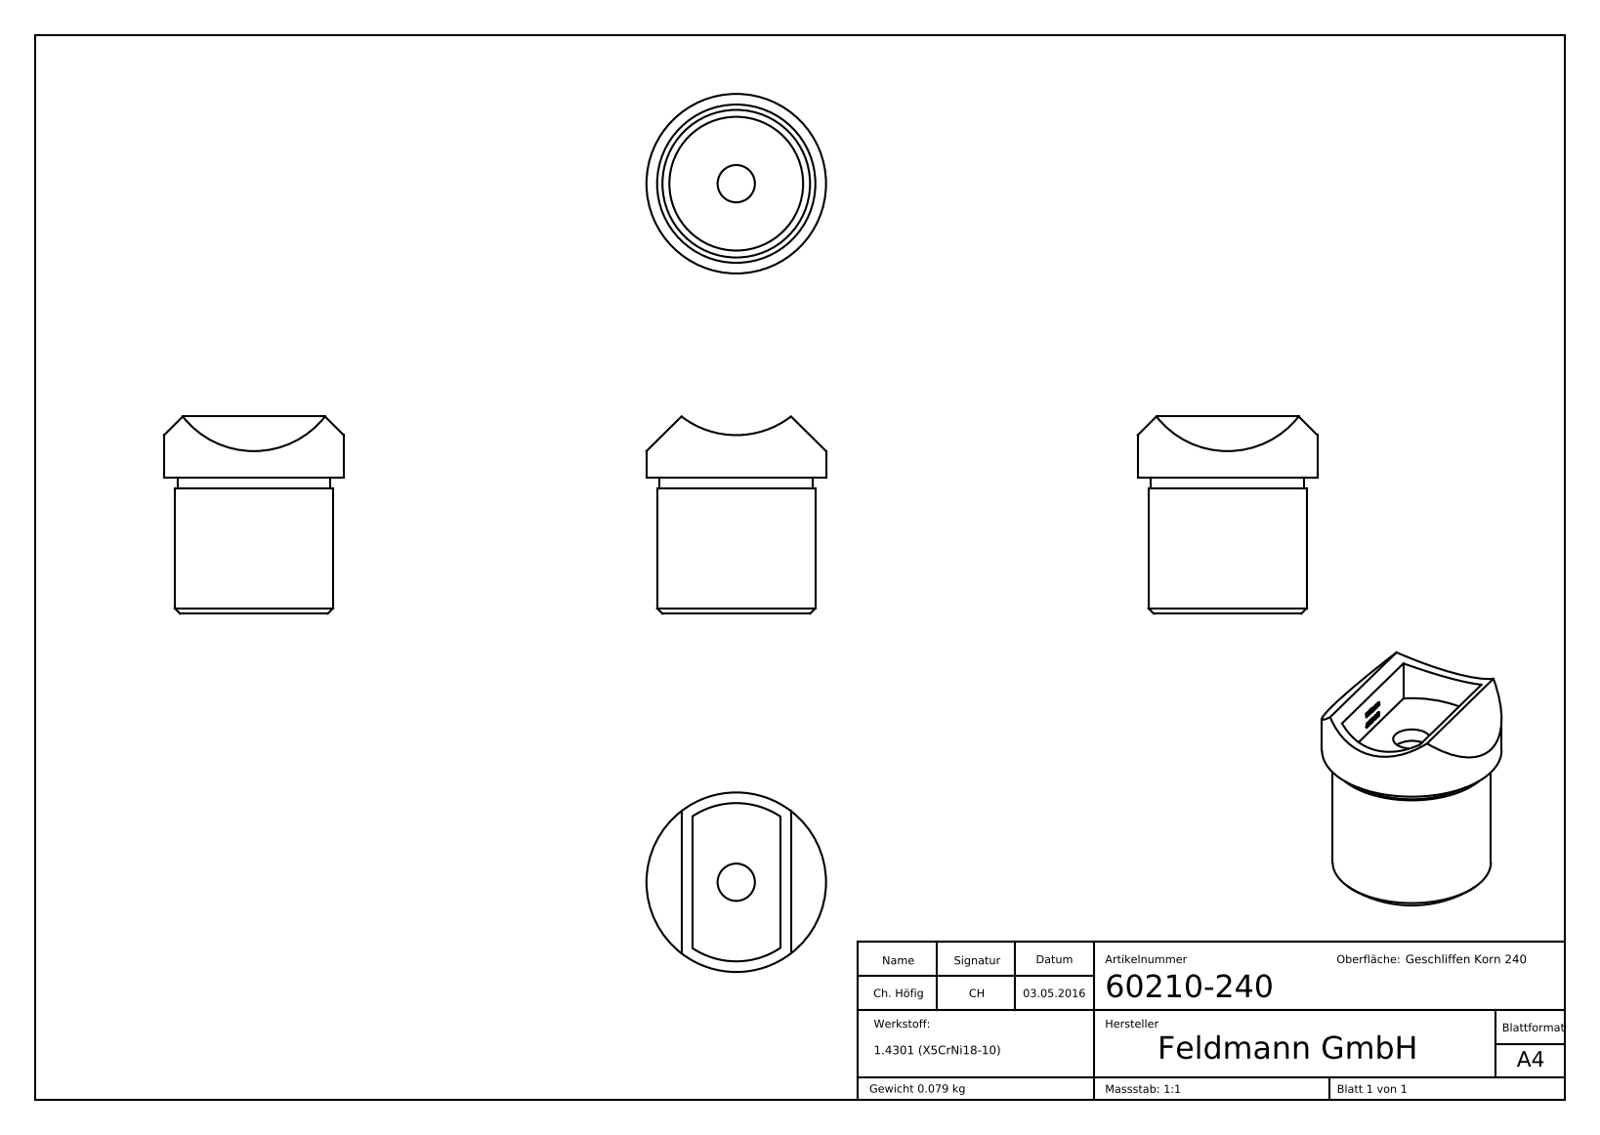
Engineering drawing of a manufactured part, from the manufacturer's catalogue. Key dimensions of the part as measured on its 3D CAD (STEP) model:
Part name (STEP PRODUCT): 60210-240
STEP written by: SolidWorks 2015 (CONFIG_CONTROL_DESIGN)
Units: millimetres
Bodies: 1 solid, 237 faces (126 planar, 13 cylindrical, 98 other)
Overall size (bounding box): 37 × 33.7 × 33.7
Volume: 9 966 mm³ · Surface area: 7 762 mm²
Round holes (diameter × count): ⌀7 ×1, ⌀25.1 ×1, ⌀29.7 ×1
Round bosses / shafts (diameter × count): ⌀33.7 ×1, ⌀28.7 ×1
Partial cylindrical surfaces — rounded edges, fillets, slot ends (radius × count): R16.85 ×1
Main face-to-face distances: 2.5, 16.56, 25.5, 28, 2, 23.5, 4.5, 16.66, 1.78, 2.33
